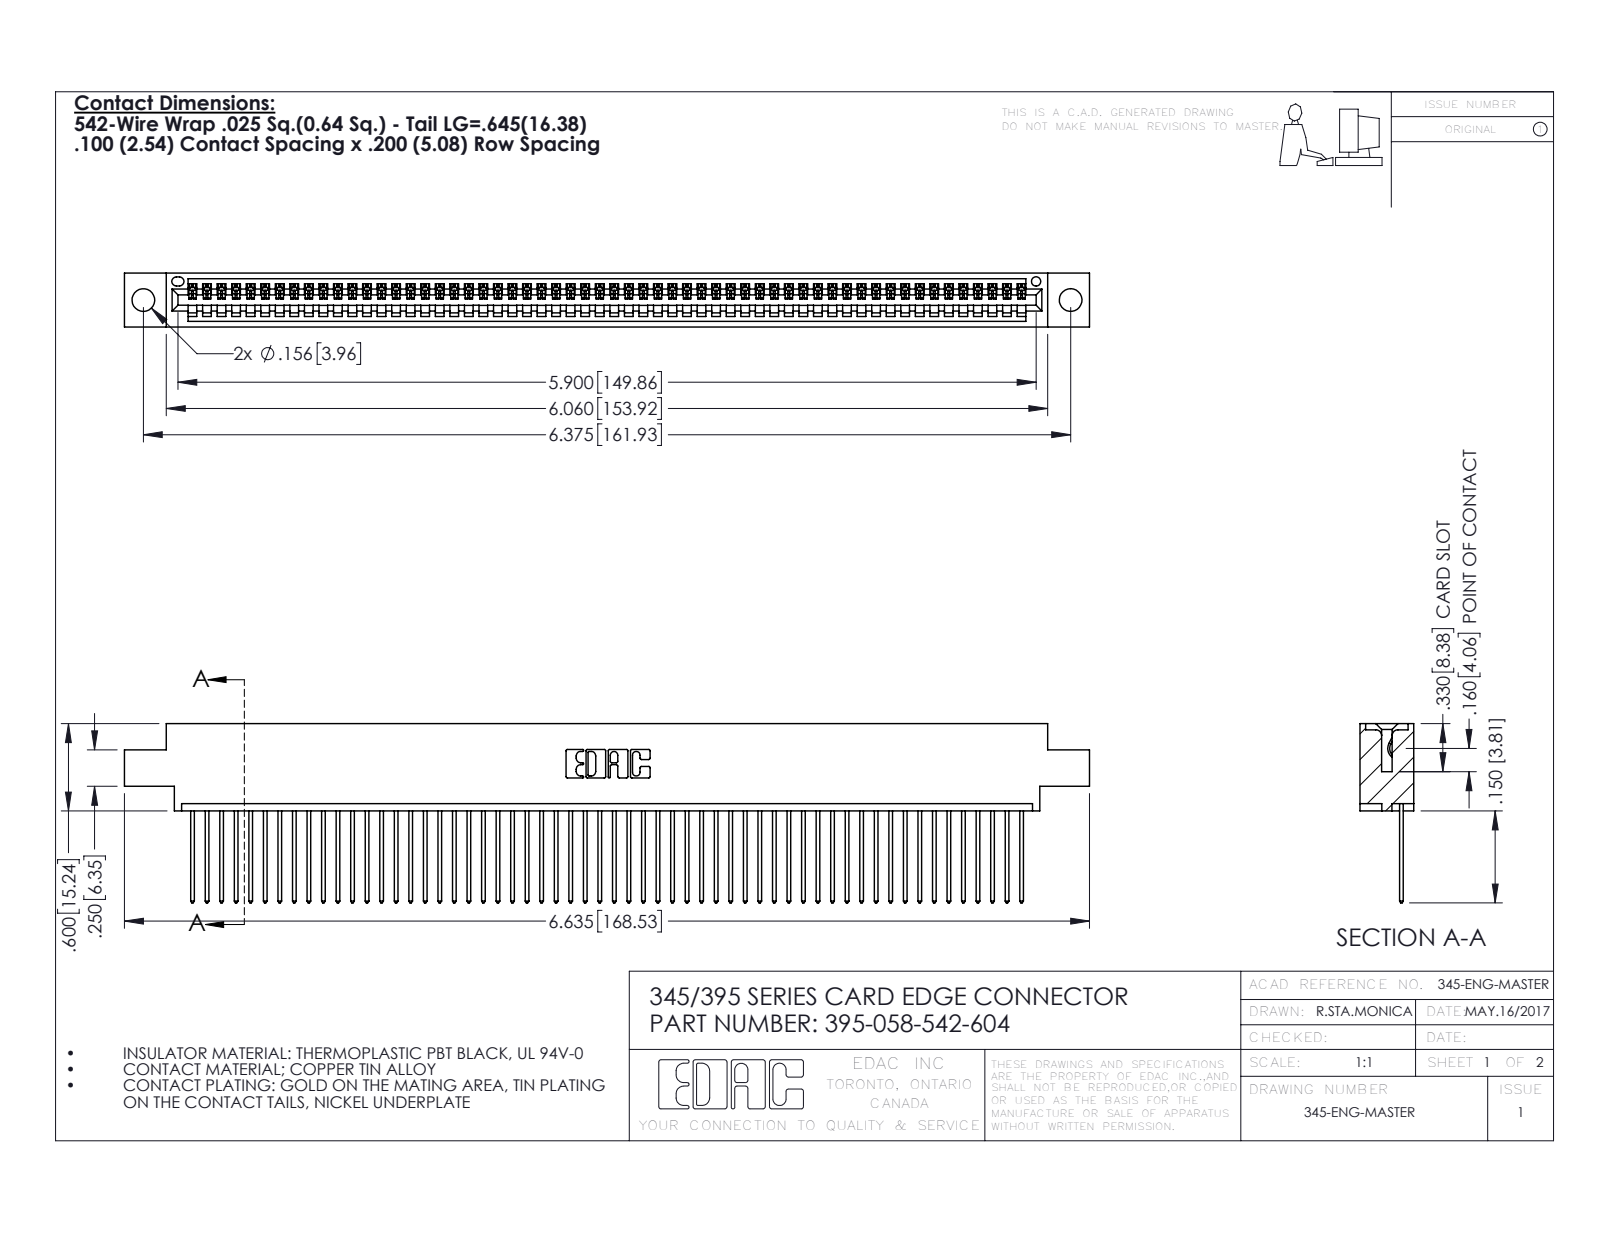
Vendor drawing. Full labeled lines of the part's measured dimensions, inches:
Part name (STEP PRODUCT): 395-058-542-604; 345-292-001_345-293-142; 345 Part_0.170 Offset - 0.156 Dia-TH
STEP written by: SolidWorks 2016 (CONFIG_CONTROL_DESIGN)
Units: inches
Bodies: 59 solids, 3494 faces (2404 planar, 1090 cylindrical, 0 other)
Overall size (bounding box): 6.635 × 1.232 × 0.37
Volume: 0.98 in³ · Surface area: 34.59 in²
Round holes (diameter × count): ⌀0.156 ×2, ⌀0.064 ×1
Partial cylindrical surfaces — rounded edges, fillets, slot ends (radius × count): R0.006 ×116, R0.01 ×116, R0.01 ×22, R0.007 ×6, R0.031 ×6, R0.026 ×3, R0.031 ×2, R0.04 ×2
Main face-to-face distances: 0.072, 0.298, 0.37, 0.098, 0.272, 0.025, 0.2, 0.225, 0.175, 0.149
Hole centre spacings: 0.27, 6.139, 6.375
